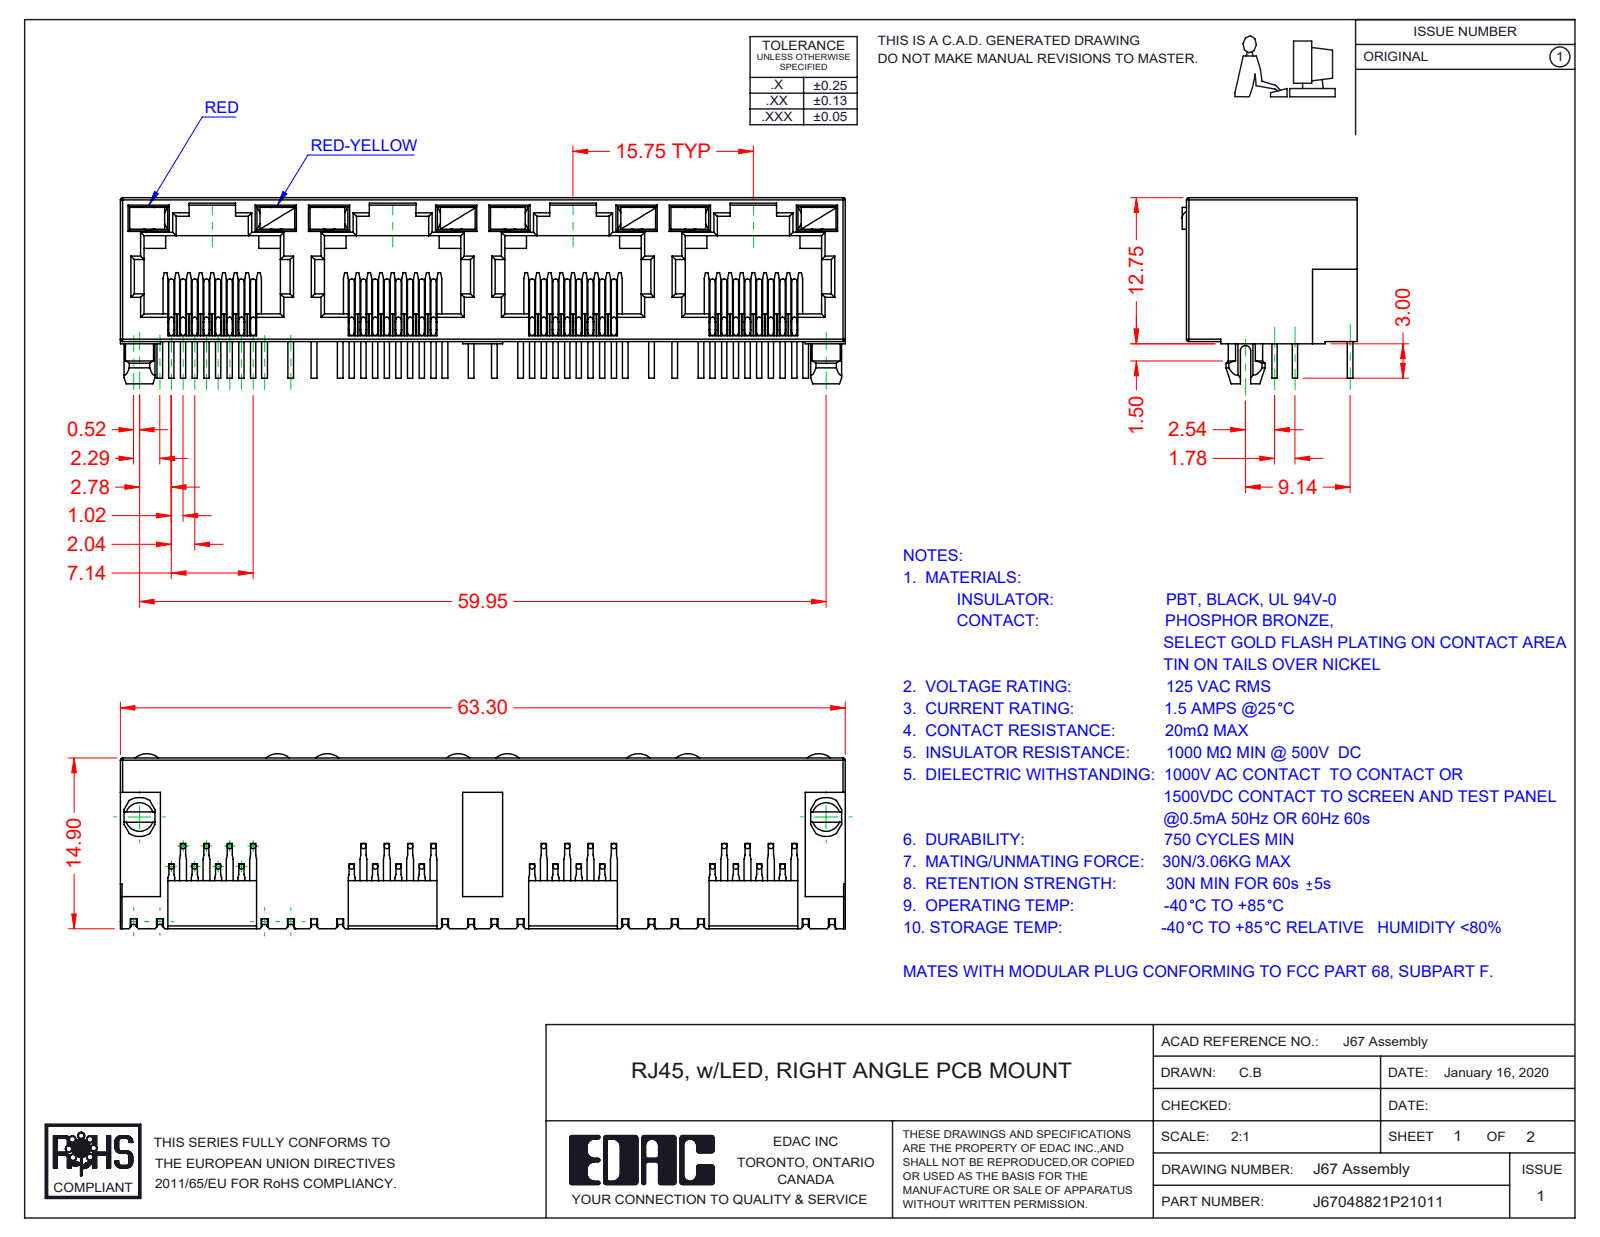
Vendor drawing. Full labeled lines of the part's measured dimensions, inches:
Part name (STEP PRODUCT): 67 Insulator; 67 LED RH_8-Red-Yellow; 67 LED LH_2-Red; 67 Contacts (+1 more)
STEP written by: SolidWorks 2016 (CONFIG_CONTROL_DESIGN)
Units: inches
Bodies: 41 solids, 2473 faces (1781 planar, 484 cylindrical, 208 other)
Overall size (bounding box): 2.492 × 0.64 × 0.602
Volume: 0.315 in³ · Surface area: 17.94 in²
Round bosses / shafts (diameter × count): ⌀0.018 ×96
Partial cylindrical surfaces — rounded edges, fillets, slot ends (radius × count): R0.008 ×66, R0.012 ×29, R0.018 ×9, R0.061 ×8, R0.059 ×2, R0.067 ×2, R0.014 ×1, R0.039 ×1
Main face-to-face distances: 0.02, 0.494, 0.074, 0.035, 0.394, 0.62, 0.039, 0.055, 0.433, 0.468
